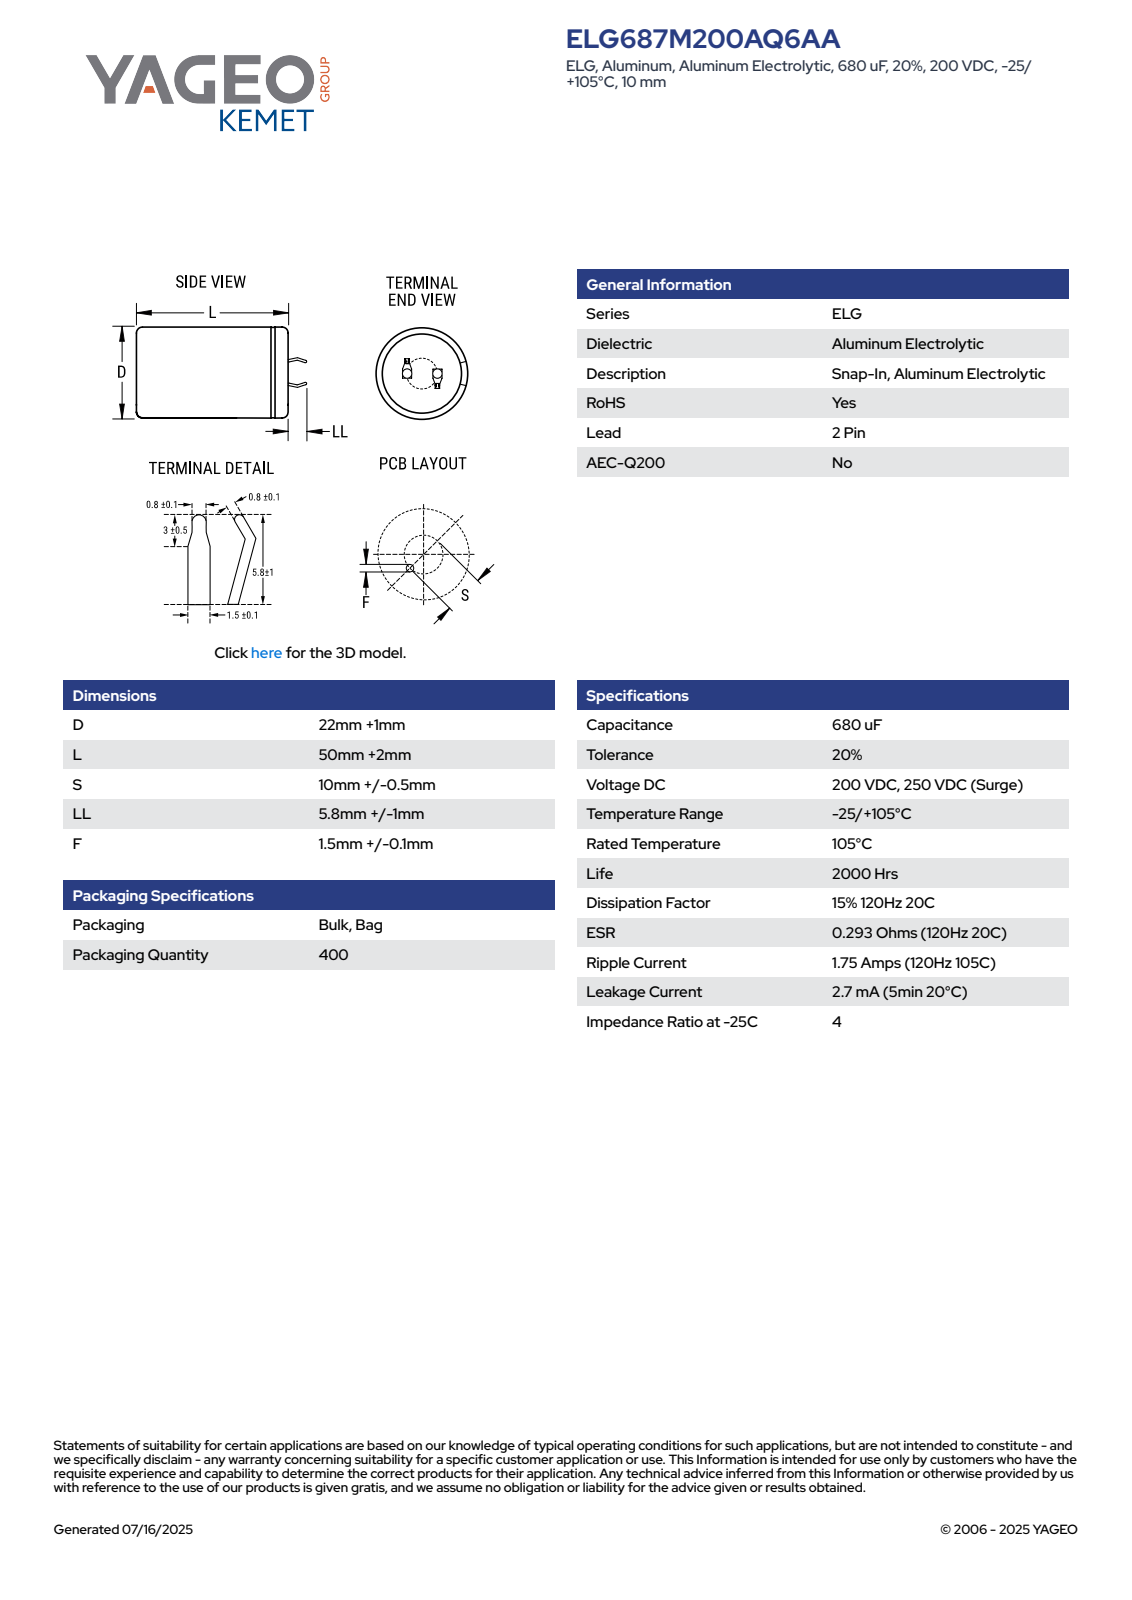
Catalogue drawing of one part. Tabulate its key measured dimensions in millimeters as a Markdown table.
| quantity | value |
| --- | --- |
| part name | CARS_K2P_22X50_D23L52S10LL6.8F1.6 |
| STEP written by | SolidWorks 2014 (AUTOMOTIVE_DESIGN) |
| units | millimeters |
| bodies | 1 solid, 100 faces (52 planar, 9 cylindrical, 39 other) |
| overall size | 58.79 × 23 × 23 |
| volume | 21 475 mm³ |
| surface area | 4 613 mm² |
| round holes (diameter × count) | 20.35 × 1 |
| round bosses / shafts (diameter × count) | 23 × 1 |
| partial cylindrical surfaces (radius × count) | 11.49 × 1 |
| main face-to-face distances | 51.99, 0.6, 52.49, 0.5, 7.08, 7.63, 0.75, 1.35, 7.68, 6.48 |
